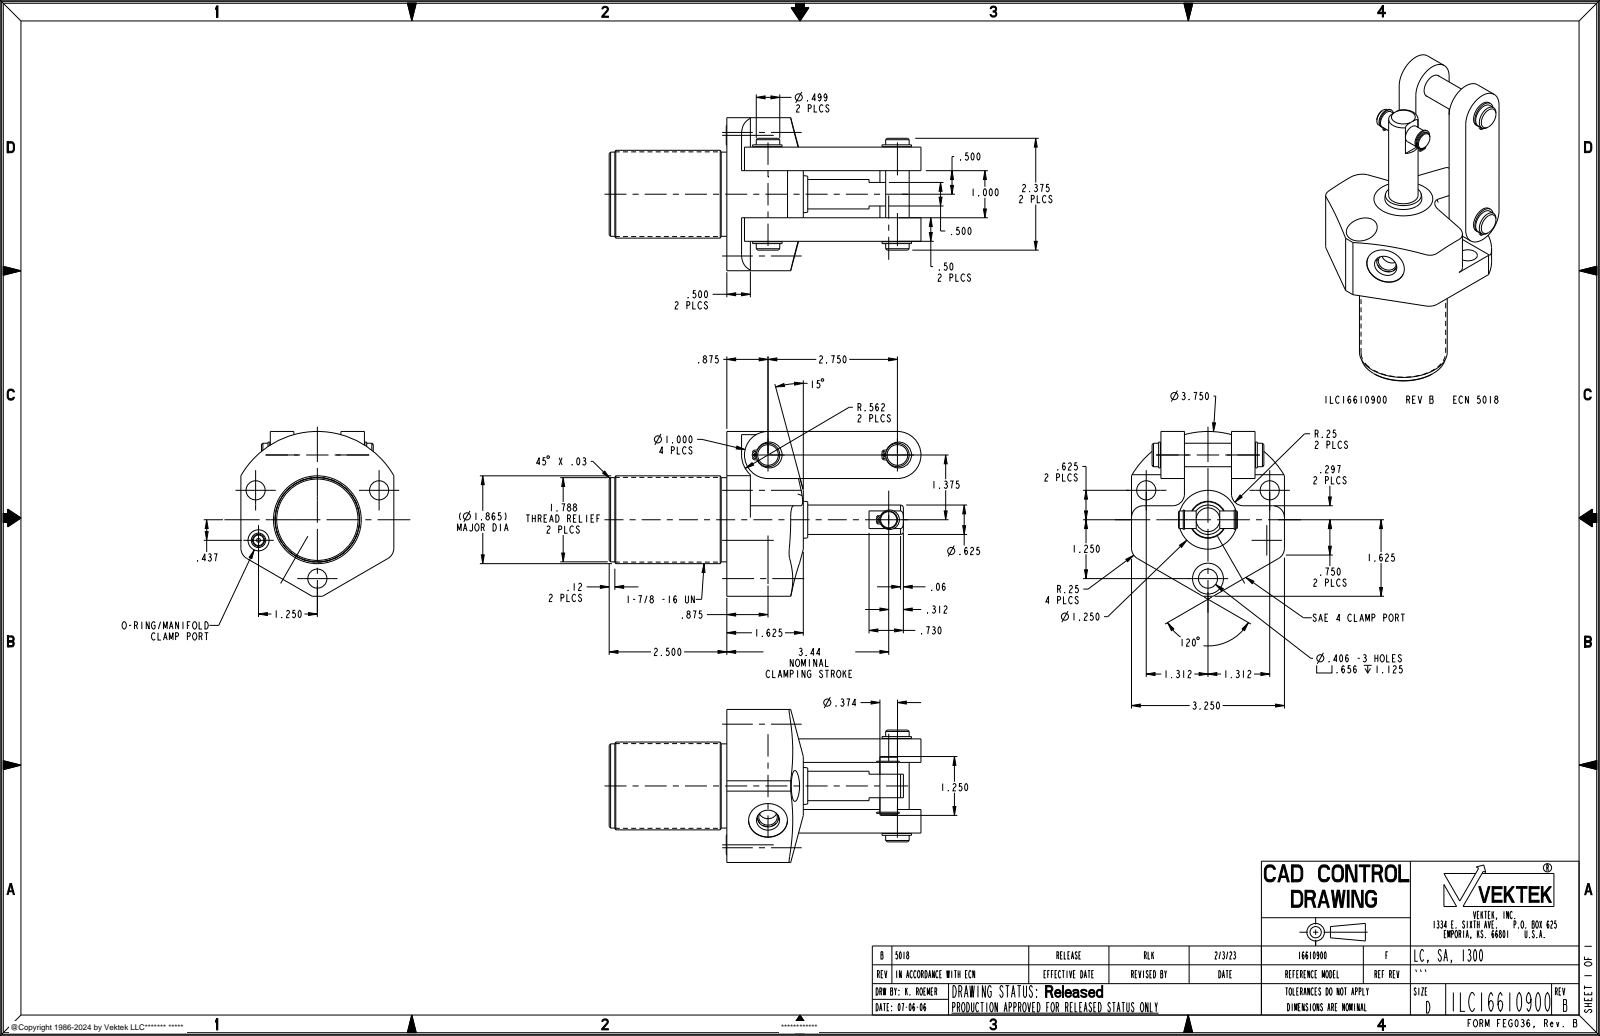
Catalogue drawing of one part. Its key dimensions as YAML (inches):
part_name: "ILC16610900"
step_written_by: "CREO PARAMETRIC BY PTC INC, 2021164 (AUTOMOTIVE_DESIGN)"
units: inches
bodies: {solids: 3, faces: 262, planar: 107, cylindrical: 119, other: 36}
overall_size: [6.625, 3.5, 3.25]
volume: 21.62
surface_area: 104
round_holes:
  - {diameter: 0.047, count: 4}
  - {diameter: 0.406, count: 3}
  - {diameter: 0.041, count: 2}
  - {diameter: 0.503, count: 2}
  - {diameter: 0.098, count: 1}
  - {diameter: 0.256, count: 1}
  - {diameter: 0.392, count: 1}
  - {diameter: 0.447, count: 1}
  - {diameter: 0.5, count: 1}
  - {diameter: 0.656, count: 1}
  - {diameter: 0.825, count: 1}
round_bosses_or_shafts:
  - {diameter: 0.549, count: 2}
  - {diameter: 0.499, count: 2}
  - {diameter: 1.865, count: 1}
  - {diameter: 1.799, count: 1}
  - {diameter: 1.788, count: 1}
  - {diameter: 0.625, count: 1}
  - {diameter: 0.438, count: 1}
  - {diameter: 0.414, count: 1}
partial_cylinders:
  - {radius: 0.047, count: 8}
  - {radius: 0.25, count: 6}
  - {radius: 0.041, count: 4}
  - {radius: 0.5, count: 2}
  - {radius: 0.562, count: 1}
  - {radius: 1.875, count: 1}
face_to_face_distances: [0.5, 1.5, 1, 1.125, 2, 0.625, 2.125, 2.625, 2.5, 3]
hole_center_spacings: [0.286, 2.75, 2.289, 2.47, 2.752, 3.031, 0.098, 0.113]
